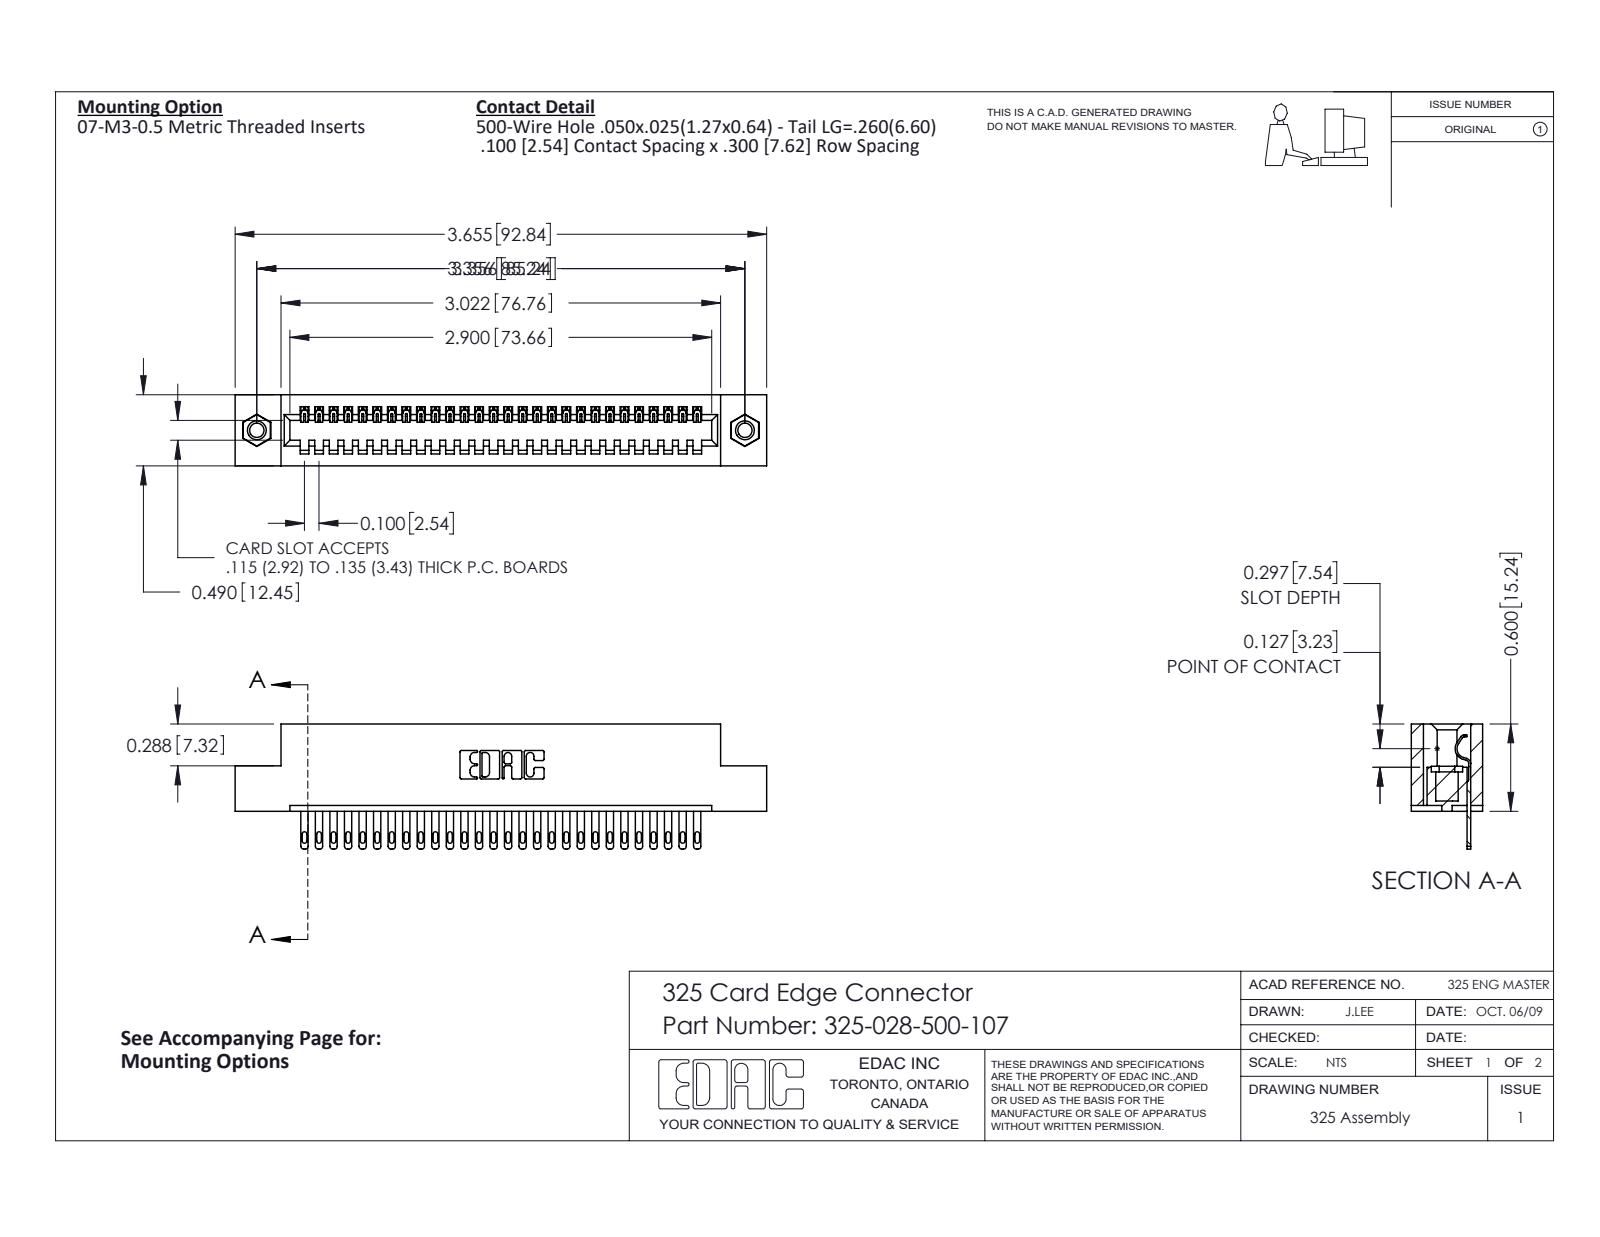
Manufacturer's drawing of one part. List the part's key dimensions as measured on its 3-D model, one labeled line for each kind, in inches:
Part name (STEP PRODUCT): 325-292-001_325-293-100; 325-028-500-107; 345-250-001_345-250-005-103; 325 Part_TI
STEP written by: SolidWorks 2016 (CONFIG_CONTROL_DESIGN)
Units: inches
Bodies: 31 solids, 1686 faces (1110 planar, 560 cylindrical, 16 other)
Overall size (bounding box): 3.655 × 0.86 × 0.49
Volume: 0.713 in³ · Surface area: 19.55 in²
Round holes (diameter × count): ⌀0.098 ×2, ⌀0.125 ×2, ⌀0.16 ×2
Round bosses / shafts (diameter × count): ⌀0.155 ×2
Partial cylindrical surfaces — rounded edges, fillets, slot ends (radius × count): R0.006 ×56, R0.016 ×56, R0.02 ×56, R0.01 ×22, R0.007 ×6, R0.031 ×6, R0.026 ×3, R0.014 ×1
Main face-to-face distances: 0.083, 0.407, 0.49, 0.3, 0.107, 0.383, 0.025, 0.325, 0.04, 0.6
Hole centre spacings: 3.356
